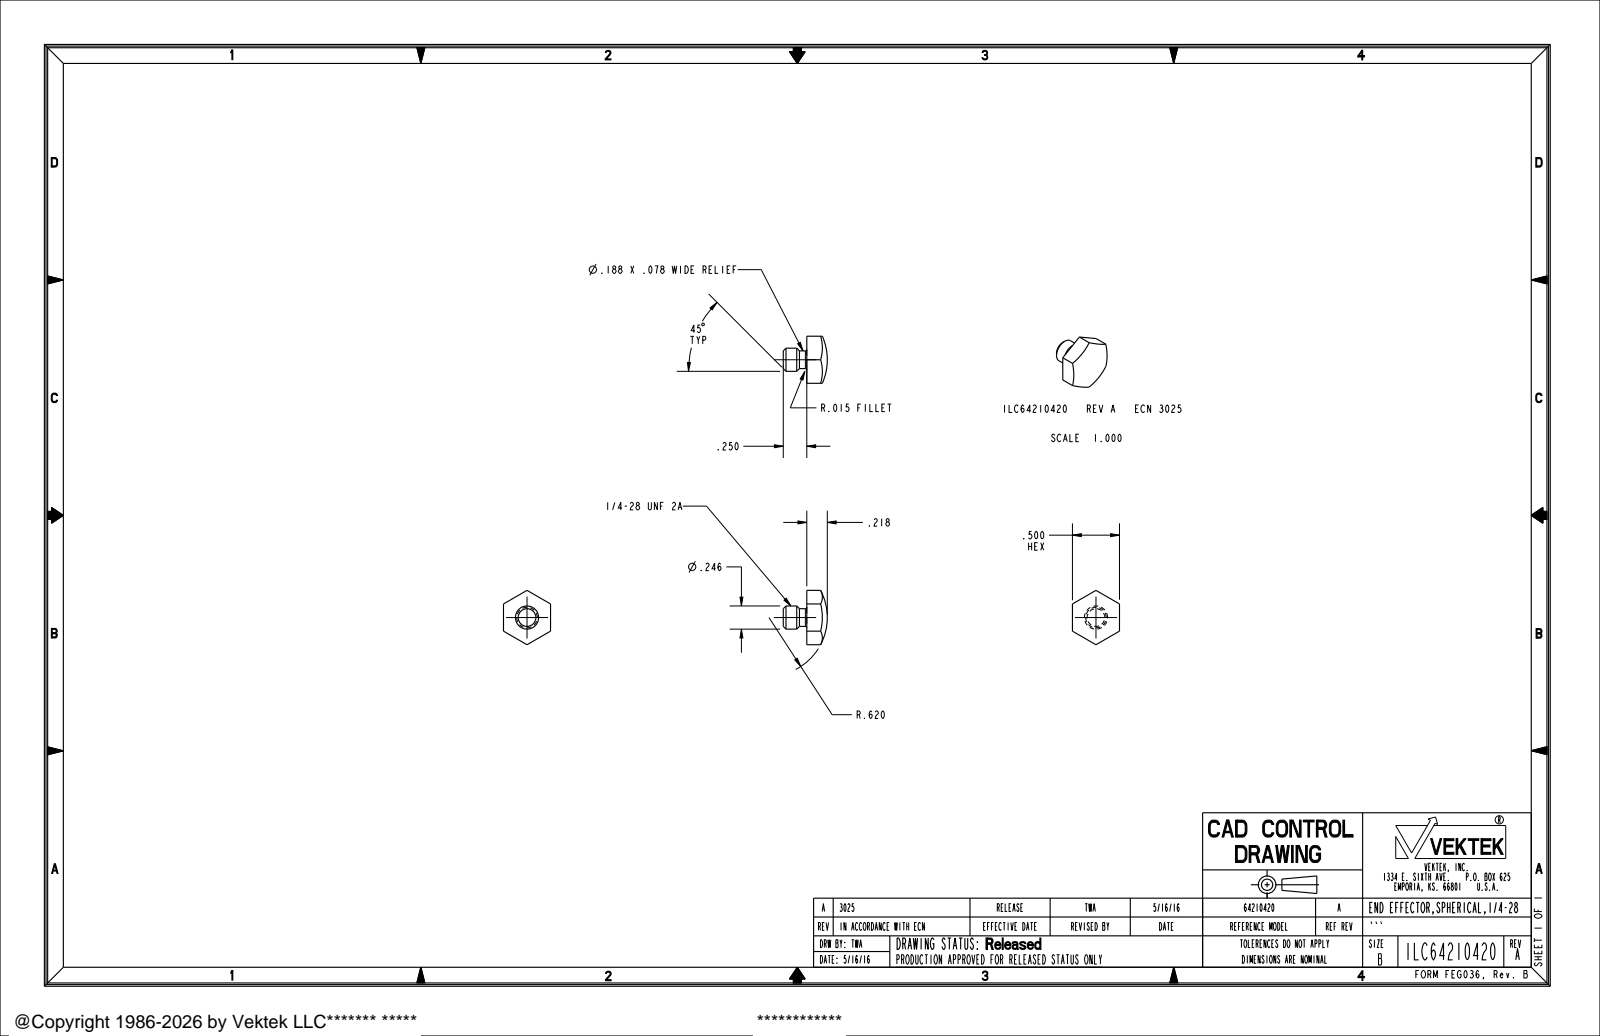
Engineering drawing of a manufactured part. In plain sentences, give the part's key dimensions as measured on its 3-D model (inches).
The part is named "ILC64210420". Its 3-D file was written by "PRO/ENGINEER BY PARAMETRIC TECHNOLOGY CORPORATION, 2013320 (CONFIG_CONTROL_DESIGN)". It is 1 solid with 20 faces: 8 planar, 4 cylindrical and 8 other. Overall it measures 0.577 by 0.5 by 0.468 inches. Its volume is 0.051 cubic inches and its surface area 0.906 square inches. Round bosses or shafts: 1 of diameter 0.246, 1 of diameter 0.188. The main face-to-face distances are 0.5, 0.25.
